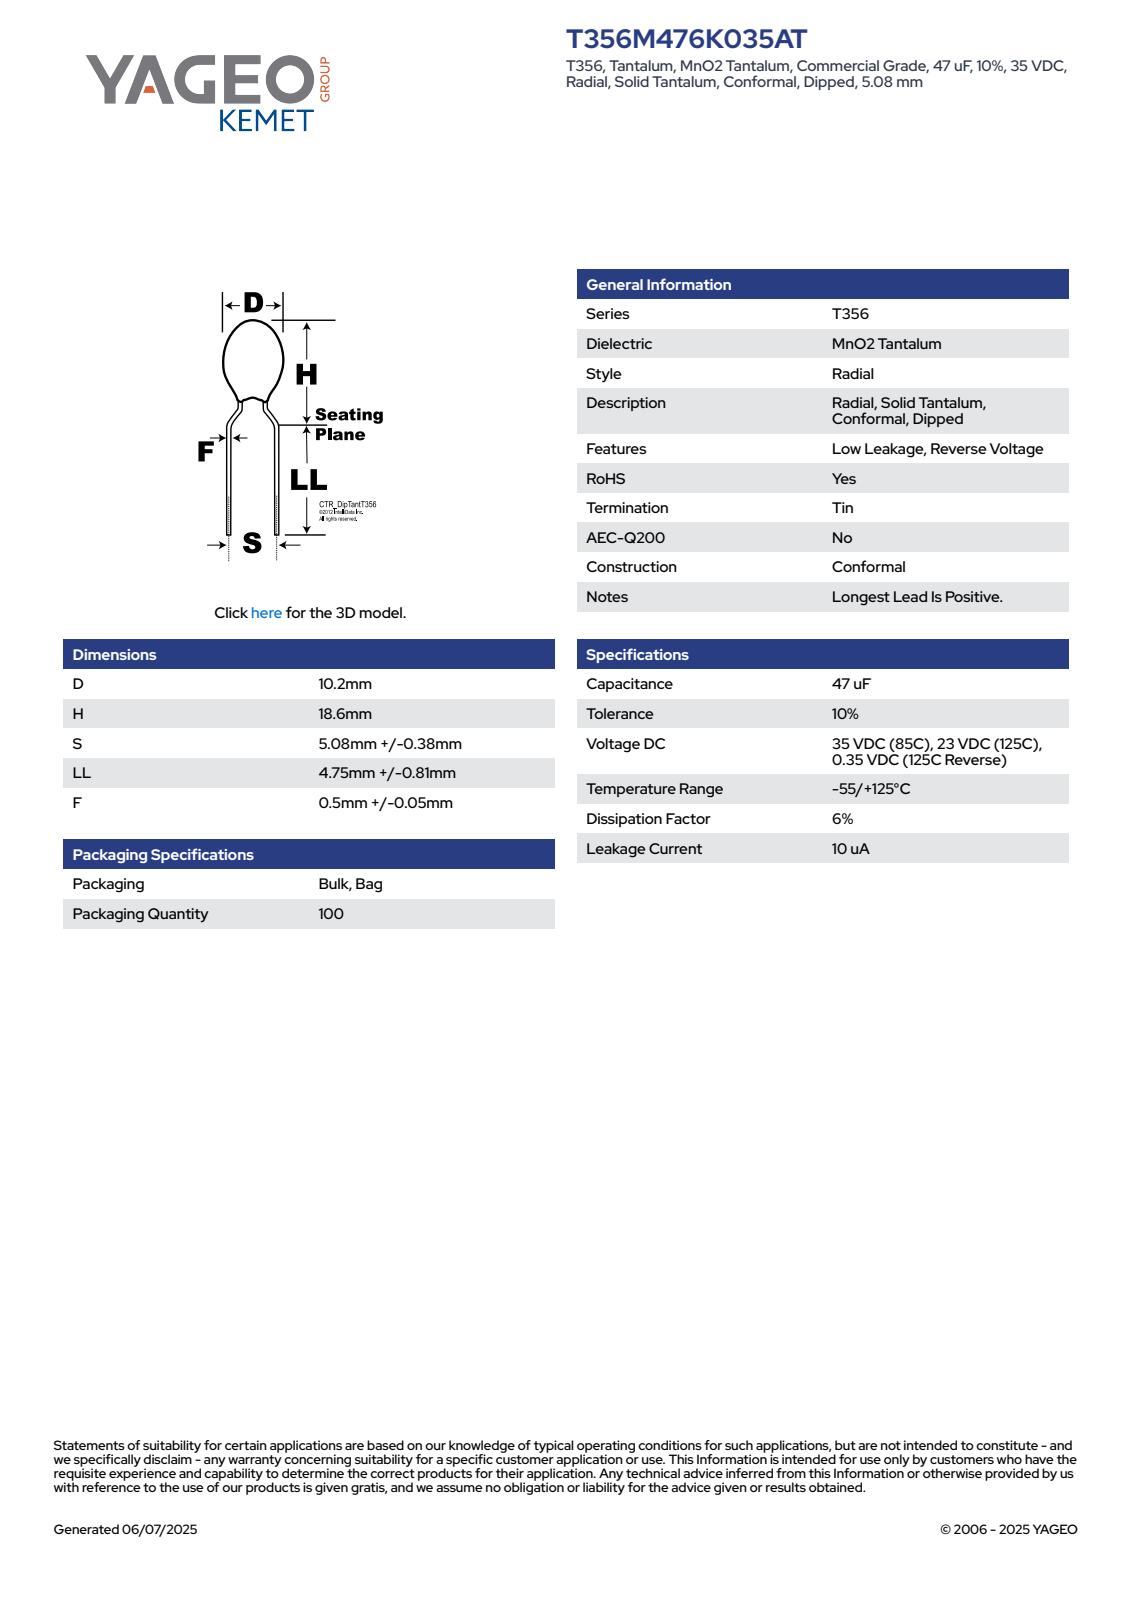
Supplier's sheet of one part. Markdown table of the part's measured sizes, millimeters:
| quantity | value |
| --- | --- |
| part name | CTR_T356_D10.2H18.6S5.08LL5.56F0.55 |
| STEP written by | SolidWorks 2014 (AUTOMOTIVE_DESIGN) |
| units | millimeters |
| bodies | 1 solid, 96 faces (27 planar, 18 cylindrical, 51 other) |
| overall size | 24.16 × 10.2 × 10.2 |
| volume | 911 mm³ |
| surface area | 516 mm² |
| round bosses / shafts (diameter × count) | 0.55 × 6, 10.2 × 1 |
| partial cylindrical surfaces (radius × count) | 5.09 × 1 |
| main face-to-face distances | 12.98, 11.18, 24.16, 19.71, 8.53, 4.45, 18.09, 6.91, 1.62, 6.07 |
